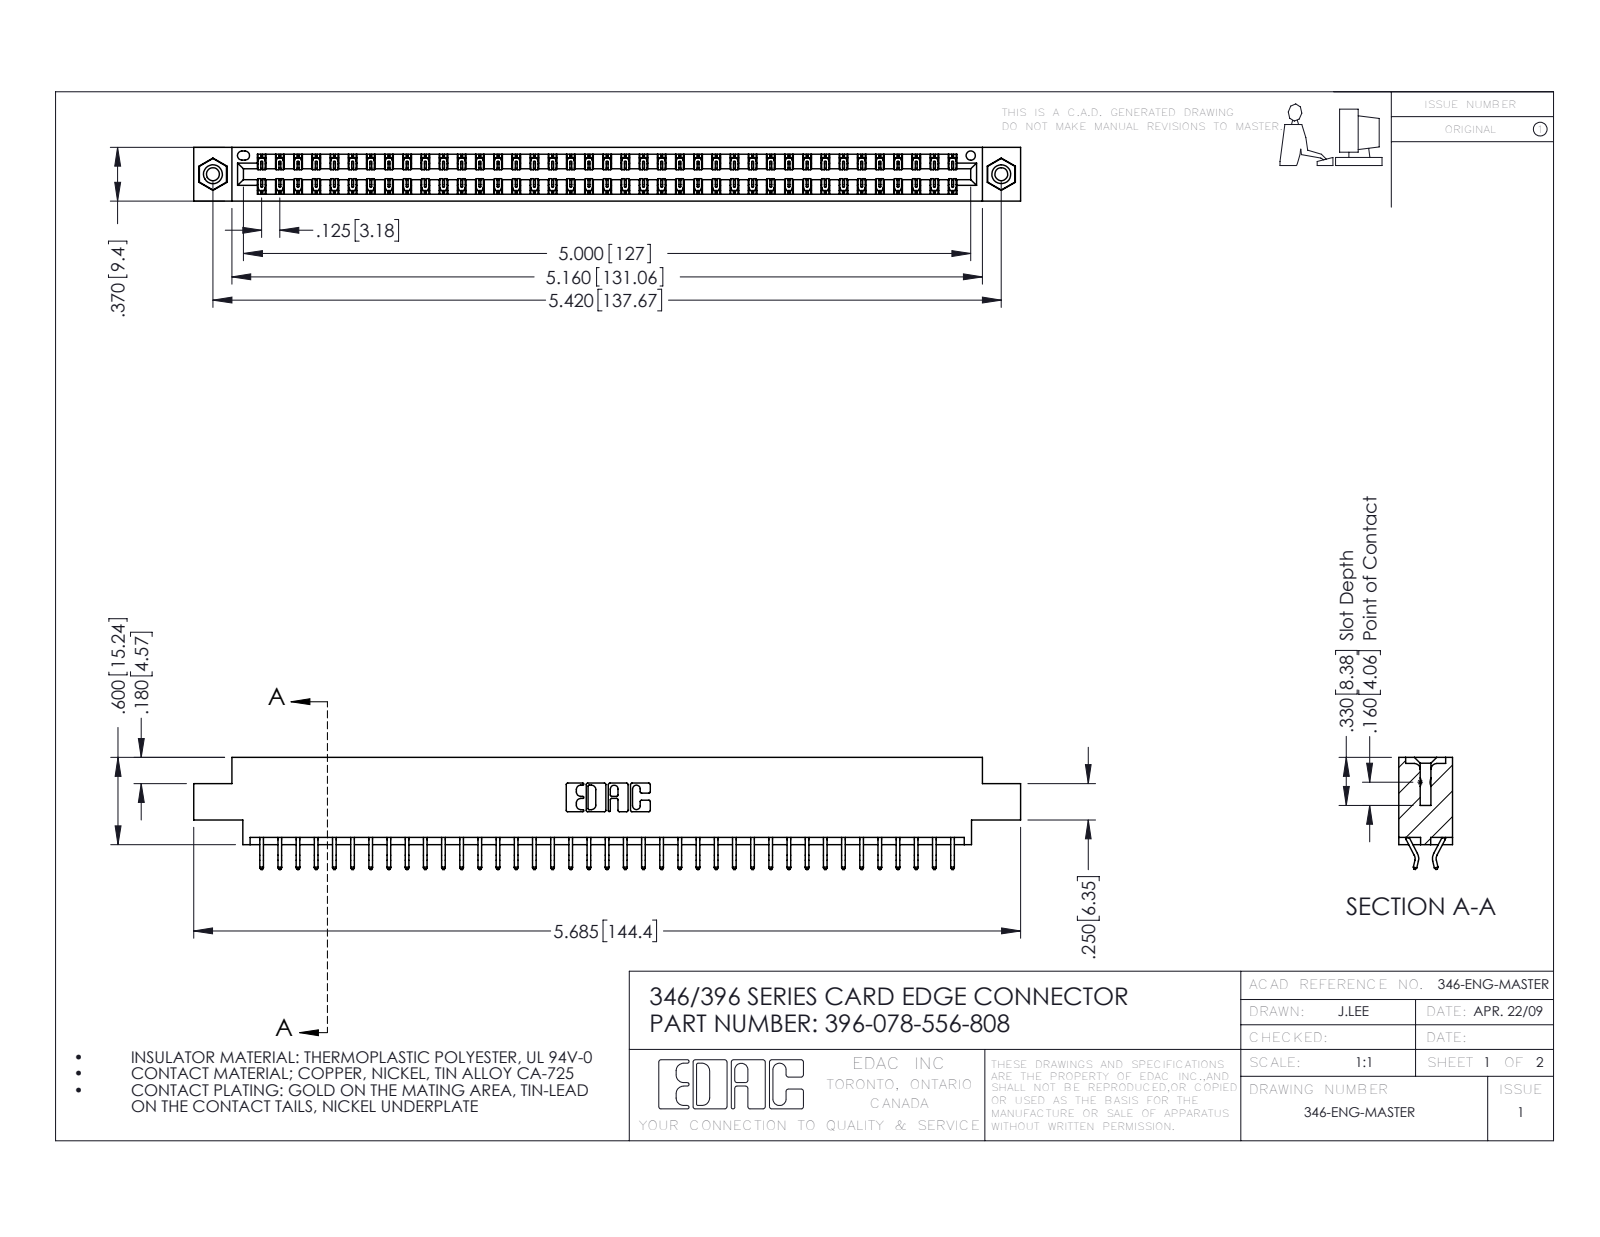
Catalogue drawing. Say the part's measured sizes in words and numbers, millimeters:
The part is named "396-078-556-808; 345-250-001_345-250-003-102; 345-292-001_556 Tail; 346 Part_0.170 Offset - 0.156 Dia-TI". Its 3-D file was written by "SolidWorks 2016 (CONFIG_CONTROL_DESIGN)". It is 81 solids with 4710 faces: 3154 planar, 1540 cylindrical and 16 other. Overall it measures 144.4 by 19.6 by 9.4 millimeters. Its volume is 13 900 cubic millimeters and its surface area 19 170 square millimeters. Round holes: 2 of diameter 2.3, 2 of diameter 3.2, 2 of diameter 4, 1 of diameter 1.6. Round bosses or shafts: 2 of diameter 3.9. Partial cylindrical surfaces (rounded edges, fillets, slot ends): 117 of radius 0.2, 22 of radius 0.3, 6 of radius 0.2, 6 of radius 0.8, 3 of radius 0.7, 2 of radius 0.3, 2 of radius 0.4, 2 of radius 0.6. The main face-to-face distances are 1.2, 8.2, 9.4, 6.4, 0.6, 1.8, 7.6, 7, 5.6, 3.8. The hole center spacings are 6.2, 132.4, 137.7.
